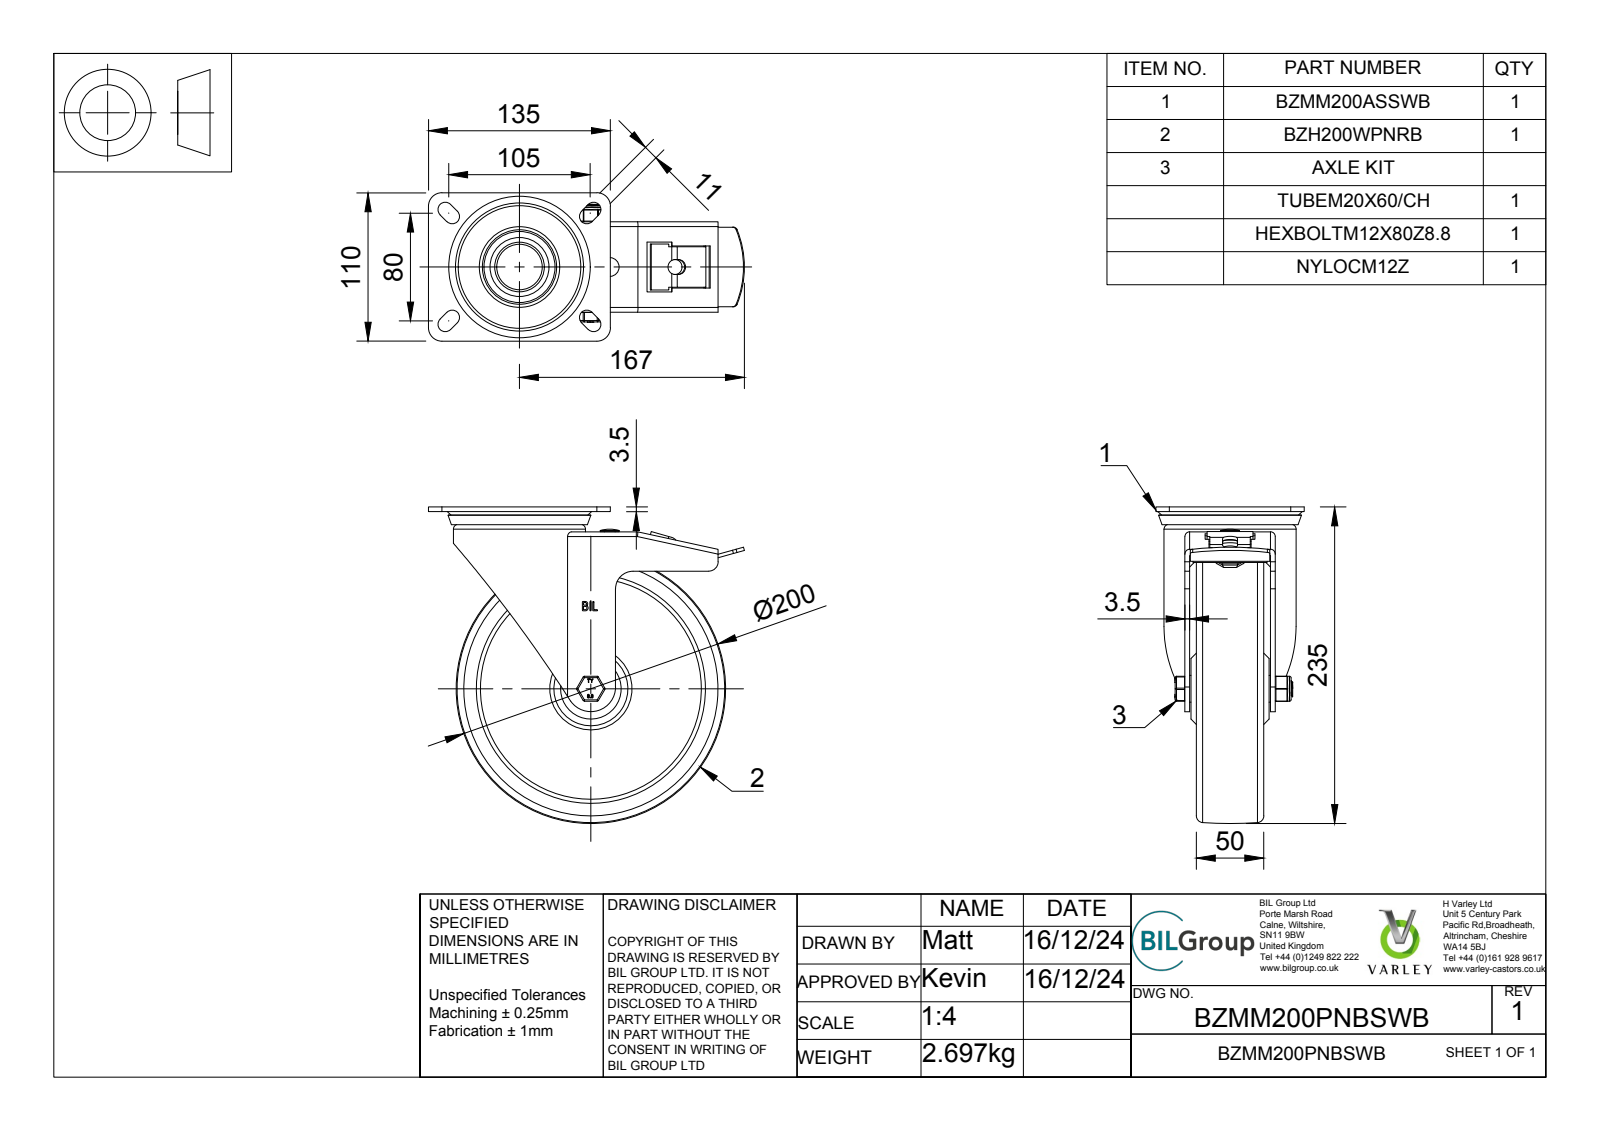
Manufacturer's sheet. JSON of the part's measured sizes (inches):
{"part_name": "BZMM200PNBSWB v3; BZMM200ASSWB v1; ZINC PLATED, PRESSED STEEL TOP PLATE; ZINC PLATED, PRESSED STEEL TOP PLATE Geometry (+7 more)", "step_written_by": "Autodesk Translation Framework v13.20.0.188 (AP242_MANAGED_MODEL_BASED_3D_ENGINEERING_MIM_LF)", "units": "inches", "bodies": {"solids": 66, "faces": 678, "planar": 332, "cylindrical": 206, "other": 140}, "overall_size": [9.252, 9.232, 4.331], "volume_in3": 61.27, "surface_area_in2": 549.1, "round_holes": [[0.315, 1], [0.433, 1], [0.472, 1], [0.48, 1], [0.492, 1], [0.551, 1], [0.787, 1], [0.807, 1], [1.181, 1], [1.26, 1], [1.329, 1], [2.402, 1]], "round_bosses_or_shafts": [[0.197, 10], [3.858, 1], [3.071, 1], [2.165, 1], [1.969, 1], [1.565, 1], [1.161, 1], [0.783, 1]], "partial_cylinders_radius": [[0.02, 18], [0.039, 12], [0.217, 10], [0.069, 7], [0.01, 6], [0.098, 6], [0.138, 4], [0.394, 4]], "face_to_face_distances": [0.138, 0.157, 0.354, 0.433, 0.197, 0.335, 1.102, 1.535, 0.965, 2.165], "hole_center_spacings": [2.638]}
